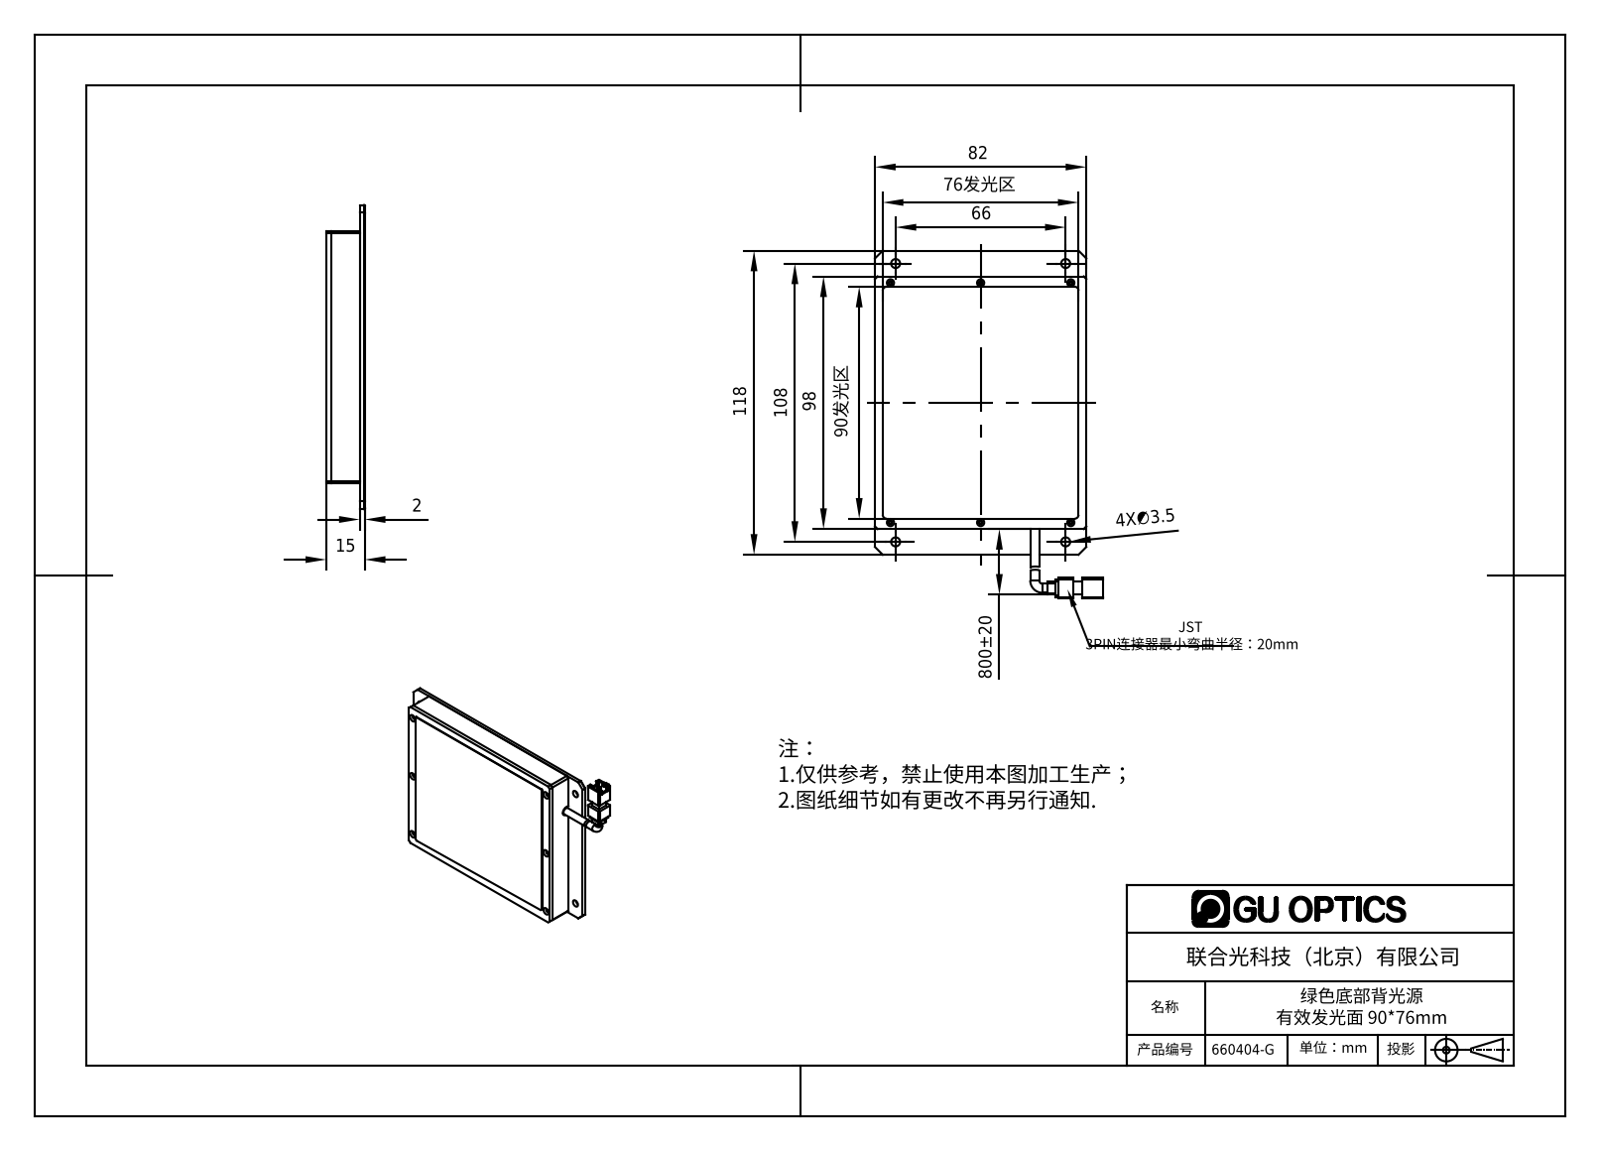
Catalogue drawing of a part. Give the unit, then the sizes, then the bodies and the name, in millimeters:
Units: millimetres
Overall size (bounding box): 135 × 88.5 × 17.6
Round holes (diameter × count): ⌀1.25 ×6, ⌀1.6 ×6, ⌀1.8 ×6, ⌀2 ×6, ⌀2.2 ×6, ⌀3.5 ×4
Round bosses / shafts (diameter × count): ⌀3.5 ×2
Partial cylindrical surfaces — rounded edges, fillets, slot ends (radius × count): R0.5 ×8, R1 ×8, R1.5 ×4, R2 ×2, R0.48 ×1, R0.52 ×1, R1.07 ×1, R1.58 ×1
Main face-to-face distances: 2, 13, 11, 2.2, 15.2, 13.2, 3, 79, 15, 82
Hole centre spacings: 35, 35.01, 100.3, 1, 94, 117.2, 121.34, 6.8
Volume: 49 972 mm³ · Surface area: 48 553 mm²
Bodies: 5 solids, 396 faces (180 planar, 106 cylindrical, 110 other)
Part name (STEP PRODUCT): 660404-B
STEP written by: SolidWorks 2016 (AUTOMOTIVE_DESIGN)
